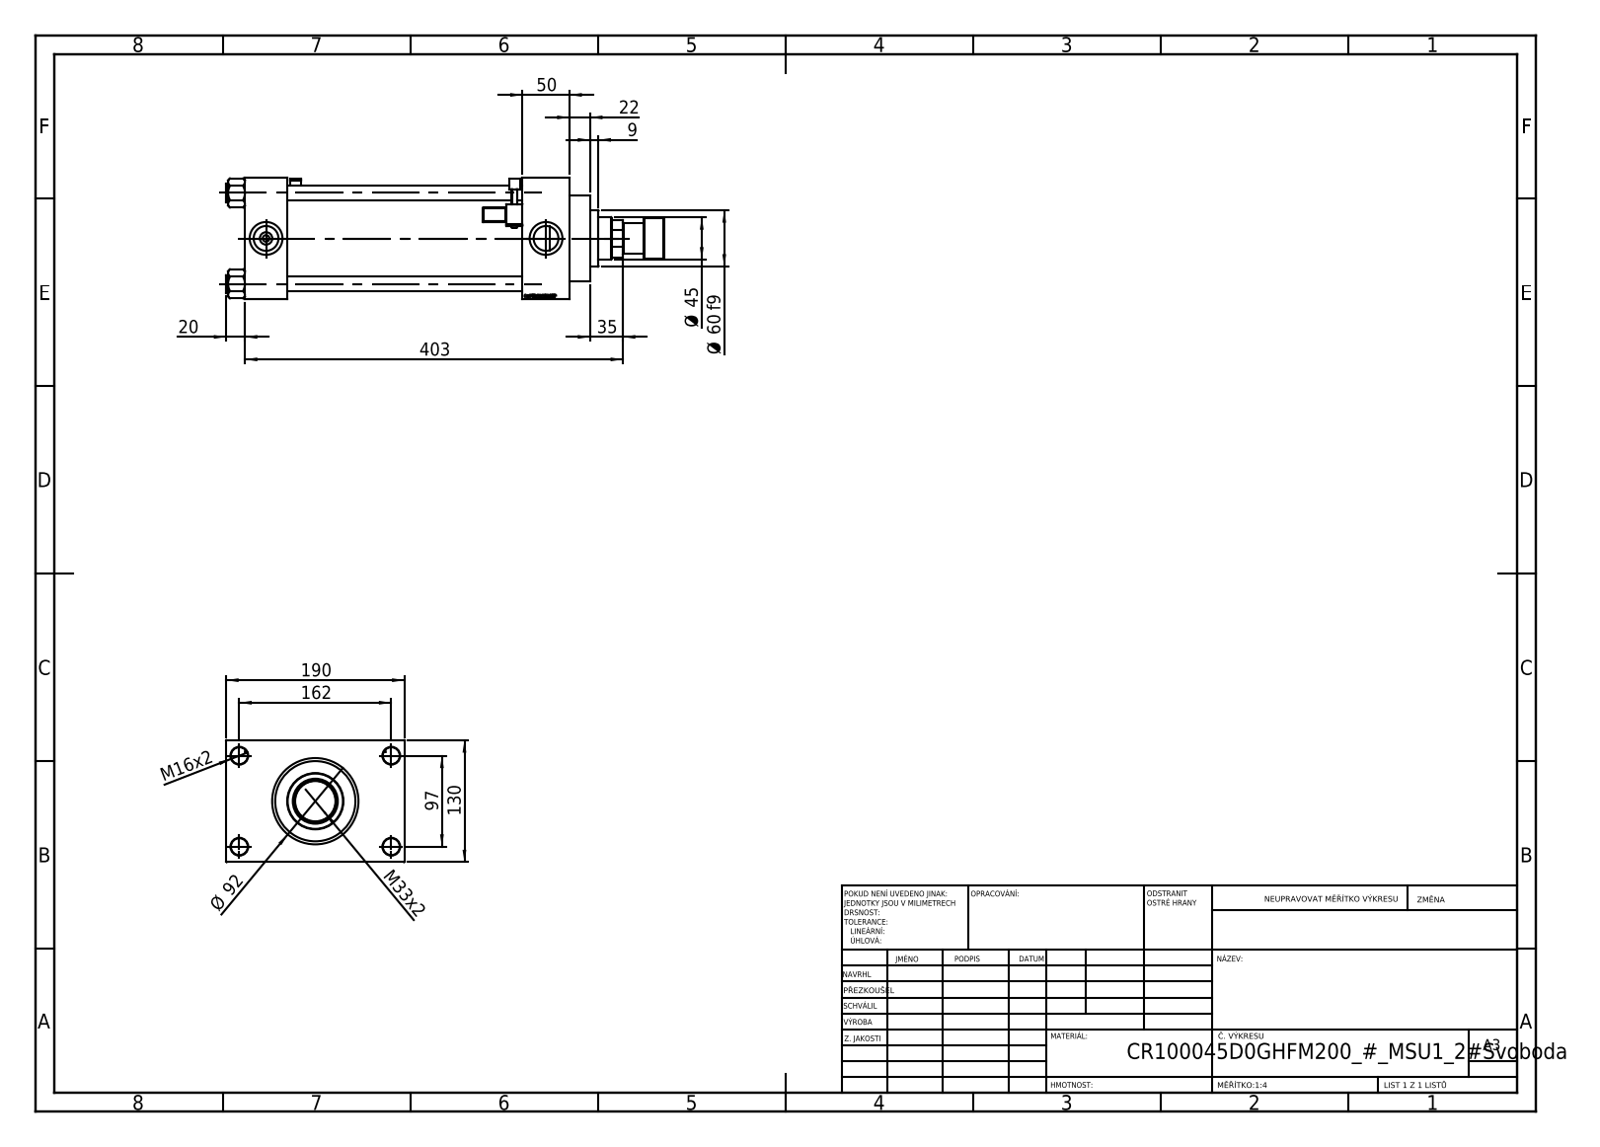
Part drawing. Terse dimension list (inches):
name: V215CR_D_TYCINKA; V215CR_ROD_END_F; V215_VC_A; V215CR_MSU (+3 more)
written by: SolidWorks 2019 (CONFIG_CONTROL_DESIGN)
unit: in
bodies: 14 solids, 1318 faces (606 planar, 152 cylindrical, 560 other)
size: 18.386 × 7.48 × 5.118
volume: 200.8 in³; area: 858.4 in²
holes: 4× ⌀0.63, 4× ⌀0.709, 2× ⌀0.276, 2× ⌀1.041, 2× ⌀1.378, 1× ⌀1.24, 1× ⌀1.772, 1× ⌀1.89, 1× ⌀2.992, 1× ⌀3.366, 1× ⌀3.937
bosses: 4× ⌀0.748, 2× ⌀0.236, 1× ⌀4.173, 1× ⌀3.622, 1× ⌀2.362, 1× ⌀1.732, 1× ⌀1.299
rounds: 48× R0.02, 2× R0.039, 2× R0.098, 2× R0.157
face distances: 5.118, 1.772, 9.882, 11.654, 13.622, 11.85, 1.969, 1.181, 6.299, 3.78
hole spacings: 1.281, 2.698, 3.717, 3.815, 4.026, 5.096, 6.367, 3.819
